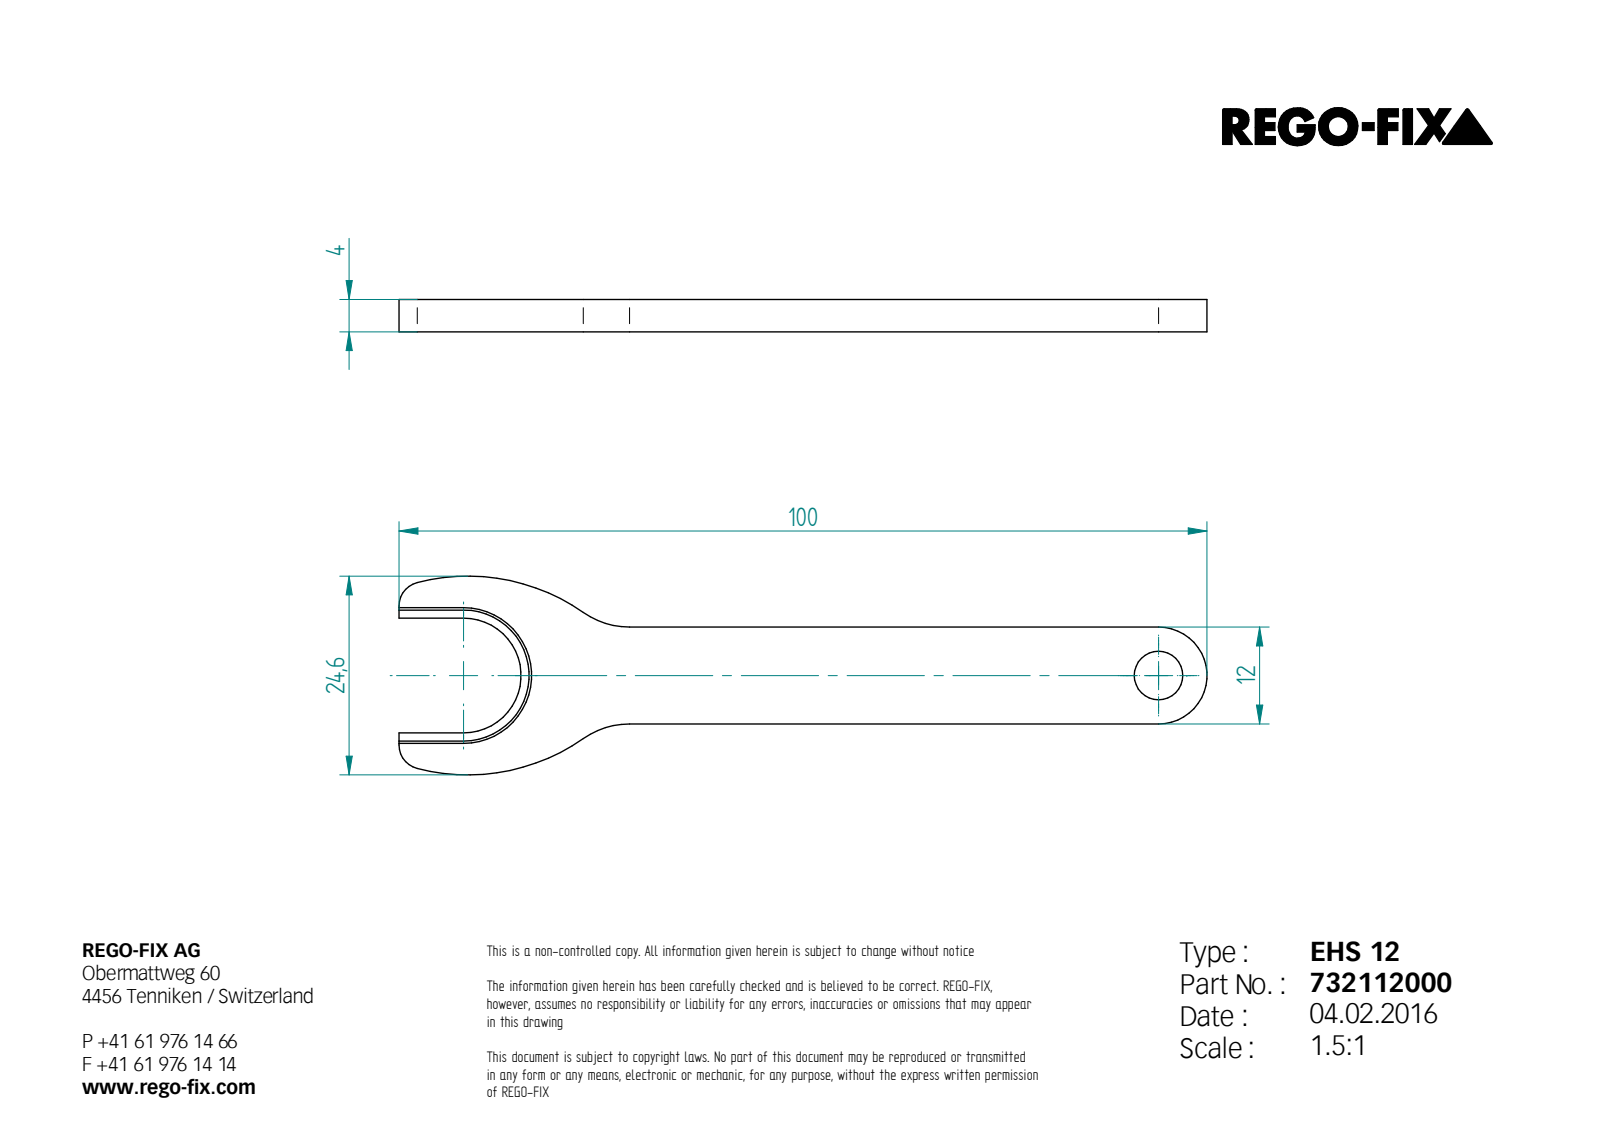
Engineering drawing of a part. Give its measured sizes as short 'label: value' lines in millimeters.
written by: Unknown (AUTOMOTIVE_DESIGN)
unit: mm
bodies: 1 solid, 23 faces (12 planar, 9 cylindrical, 2 other)
size: 100 × 24.6 × 4
volume: 4 683 mm³; area: 3 478 mm²
holes: 1× ⌀6
rounds: 2× R3, 2× R10, 2× R25, 1× R6, 1× R8.1
face distances: 4, 12, 2.1, 14.1, 16.2, 1.91
